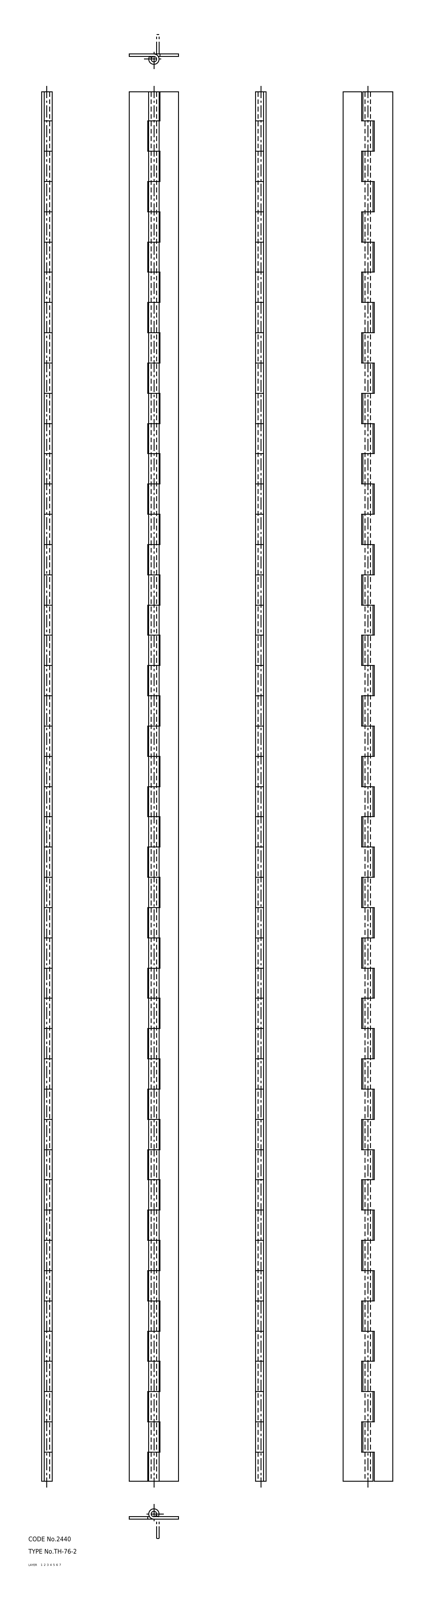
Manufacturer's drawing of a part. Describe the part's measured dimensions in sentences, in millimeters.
The part is named "shaft; TH_76_2; hinge piece_B; hinge piece_A". Its 3-D file was written by "SolidWorks 2015 (AUTOMOTIVE_DESIGN)". It is 3 solids with 288 faces: 194 planar, 94 cylindrical and 0 other. Overall it measures 900 by 32 by 6.7 millimeters. Its volume is 68 174 cubic millimeters and its surface area 92 697 square millimeters. Round holes: 1 of diameter 3.5. Round bosses or shafts: 1 of diameter 6.7. The main face-to-face distances are 1.6, 32, 12, 20, 39.2, 78.4, 117.6, 8, 156.8, 196.
